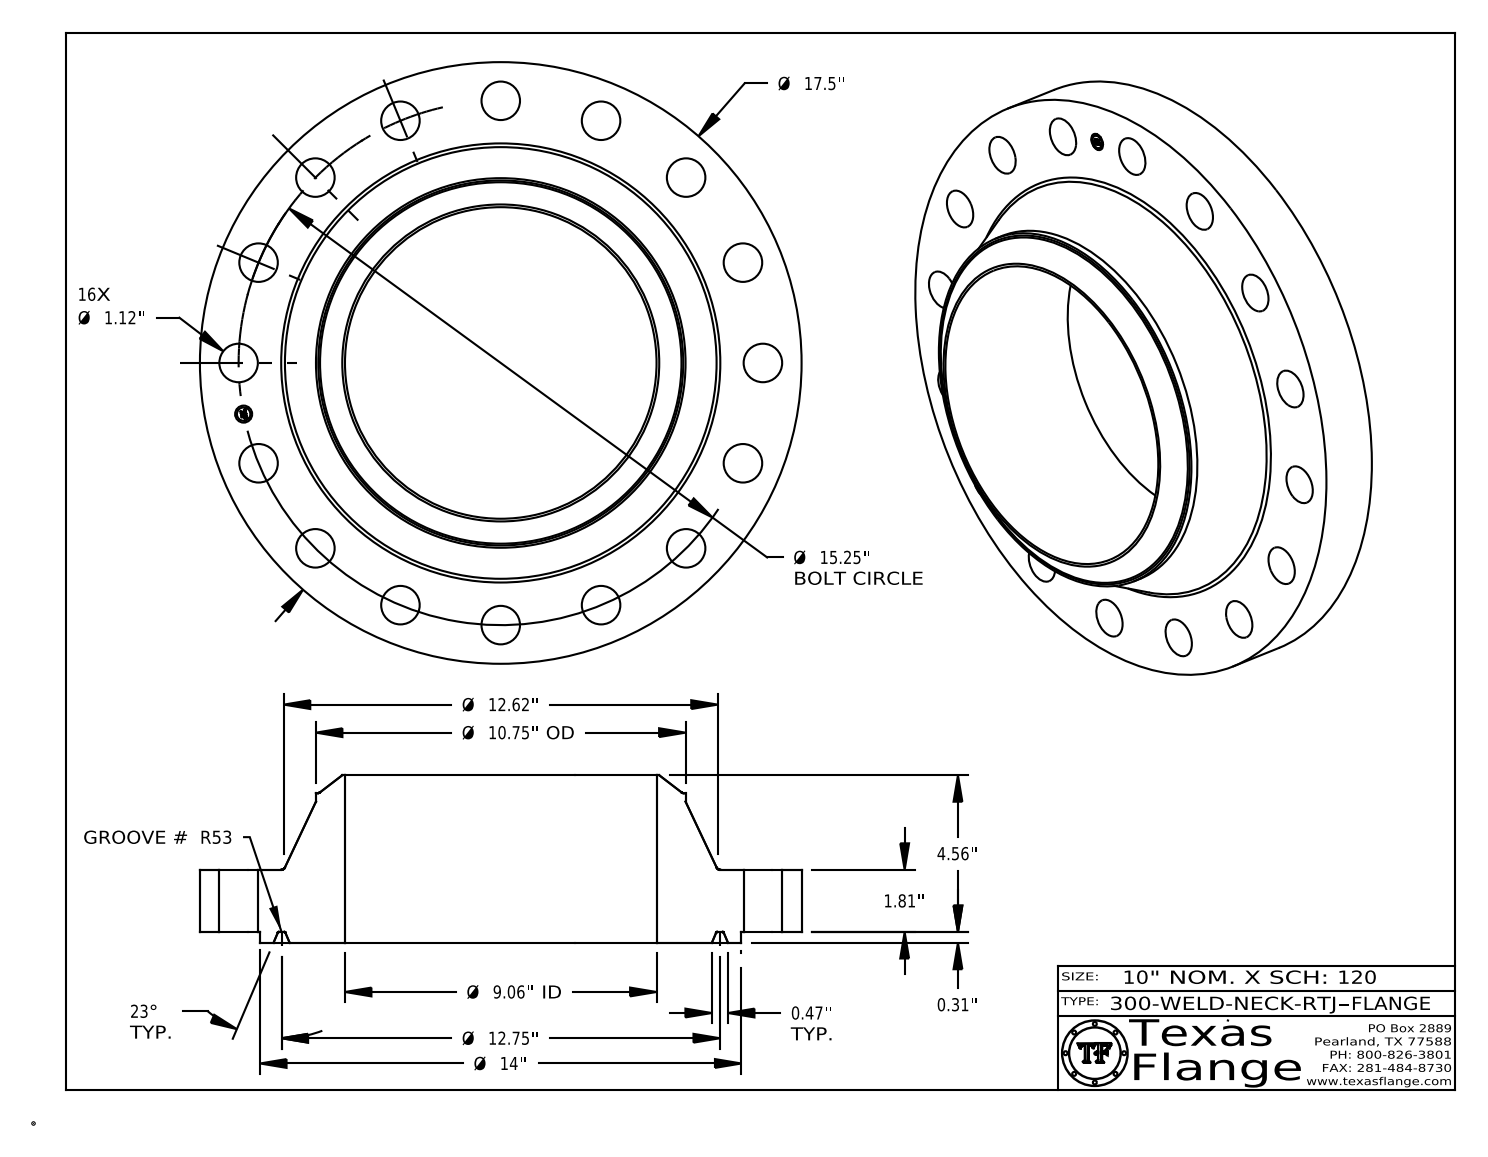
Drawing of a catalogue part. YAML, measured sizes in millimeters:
part_name: "300-WELD-NECK-RTJ"
step_written_by: "CATIA V5 STEP AP214 (AUTOMOTIVE_DESIGN)"
units: millimeters
bodies: {solids: 1, faces: 449, planar: 371, cylindrical: 60, other: 18}
overall_size: [444.5, 444.5, 123.8]
volume: 6753000
surface_area: 483700
round_holes:
  - {diameter: 28.4, count: 16}
  - {diameter: 12.6, count: 1}
  - {diameter: 230.2, count: 1}
round_bosses_or_shafts:
  - {diameter: 0.8, count: 8}
  - {diameter: 444.5, count: 1}
  - {diameter: 355.6, count: 1}
  - {diameter: 273.1, count: 1}
  - {diameter: 9.9, count: 1}
face_to_face_distances: [46, 8, 53.9, 123.8, 115.8, 69.9, 0.4, 53.5, 45.6, 70.2]
hole_center_spacings: [215.2, 273.9, 379.9, 357.9, 193.7, 75.6, 75.6, 148.2]
